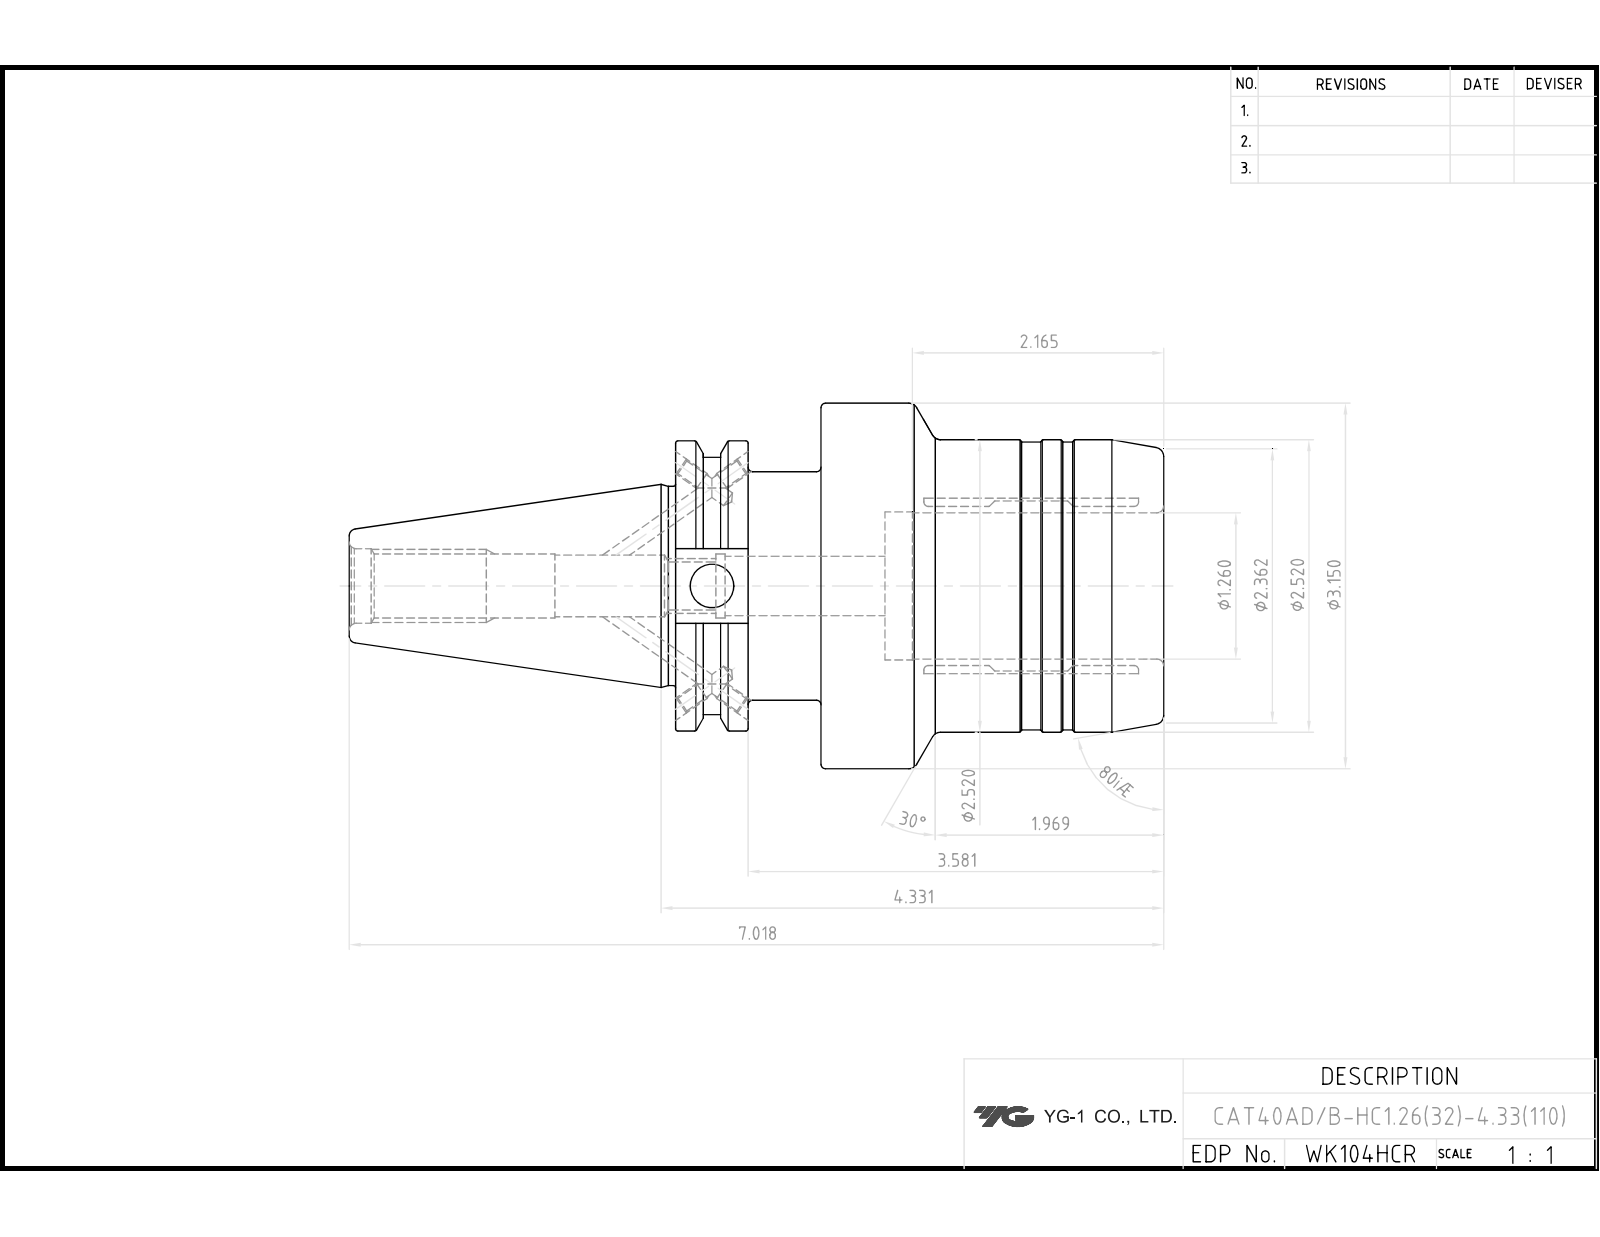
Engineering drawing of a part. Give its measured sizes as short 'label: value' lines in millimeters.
name: LO-CAT40ADB-HCR32-110
written by: Autodesk Inventor 2022 (AUTOMOTIVE_DESIGN)
unit: mm
bodies: 1 solid, 111 faces (34 planar, 35 cylindrical, 42 other)
size: 178.25 × 80 × 80
volume: 358 344 mm³; area: 51 855 mm²
holes: 4× ⌀3.24, 4× ⌀4, 1× ⌀9.53, 1× ⌀10.11, 1× ⌀13, 1× ⌀13.2, 1× ⌀13.39, 1× ⌀14, 1× ⌀16.3, 1× ⌀32
bosses: 1× ⌀80, 1× ⌀64, 1× ⌀63.5, 1× ⌀63, 1× ⌀56.3, 1× ⌀50, 1× ⌀43.6
rounds: 1× R8.19
face distances: 75, 31.83, 106.83, 45.83, 14, 61, 15.88, 15.95, 29.95, 90.95
hole spacings: 35.13
